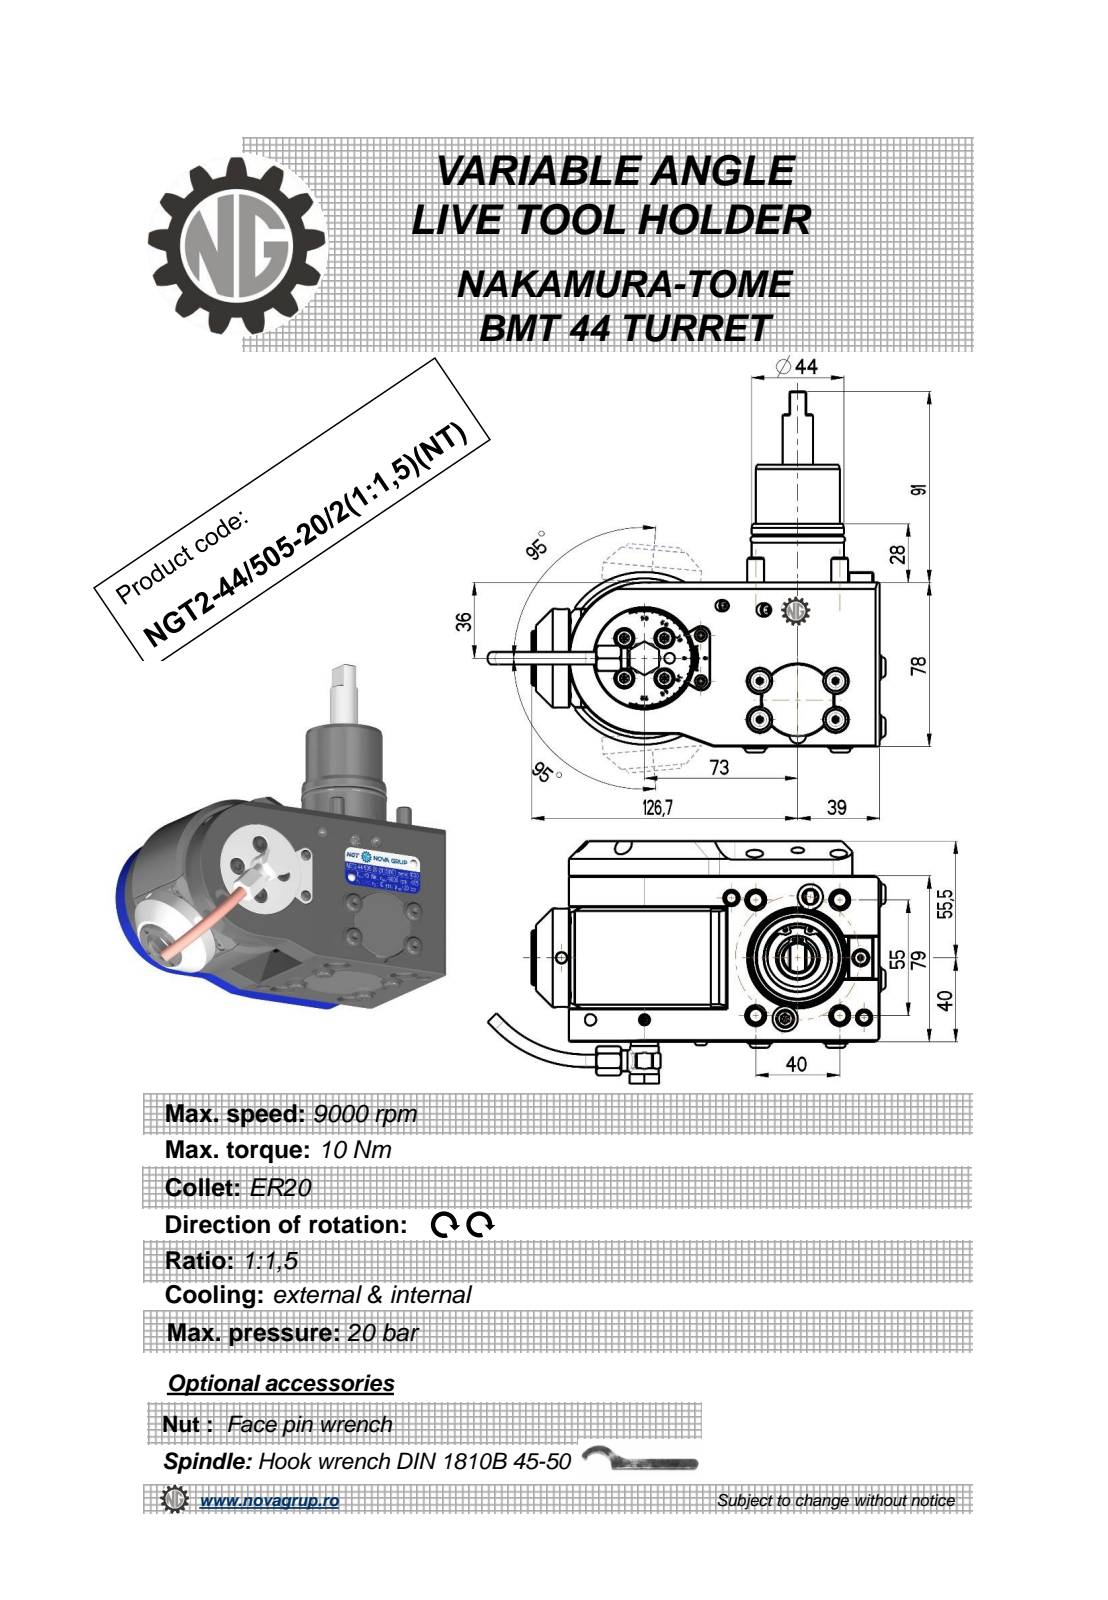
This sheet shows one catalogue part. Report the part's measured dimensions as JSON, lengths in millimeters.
{"part_name": "NGT2_44_505_20_2_1_1_5_NT", "step_written_by": "PRO/ENGINEER BY PARAMETRIC TECHNOLOGY CORPORATION, 2010280 (CONFIG_CONTROL_DESIGN)", "units": "millimeters", "bodies": {"solids": 2, "faces": 830, "planar": 401, "cylindrical": 254, "other": 175}, "overall_size": [189.42, 171.75, 115.4], "volume_mm3": 1076000, "surface_area_mm2": 91183, "round_holes": [[3.2, 4], [4, 3], [5, 2], [6.8, 2], [3, 1], [6, 1], [6.2, 1], [7.5, 1], [9, 1], [11, 1], [16, 1]], "round_bosses_or_shafts": [[11.8, 12], [9.5, 12], [8, 4], [10, 2], [5.7, 2], [47, 1], [44, 1], [40, 1]], "partial_cylinders_radius": [[0.24, 60], [8, 7], [0.14, 6], [0.5, 4], [0.8, 2], [7.7, 1], [10, 1], [12, 1]], "face_to_face_distances": [78, 16.5, 95.5, 79, 63.5, 16, 48, 15, 63, 83.7], "hole_center_spacings": [10.75, 15.2, 21.5, 50.17, 50.56, 0.4, 37.64, 38.25]}
